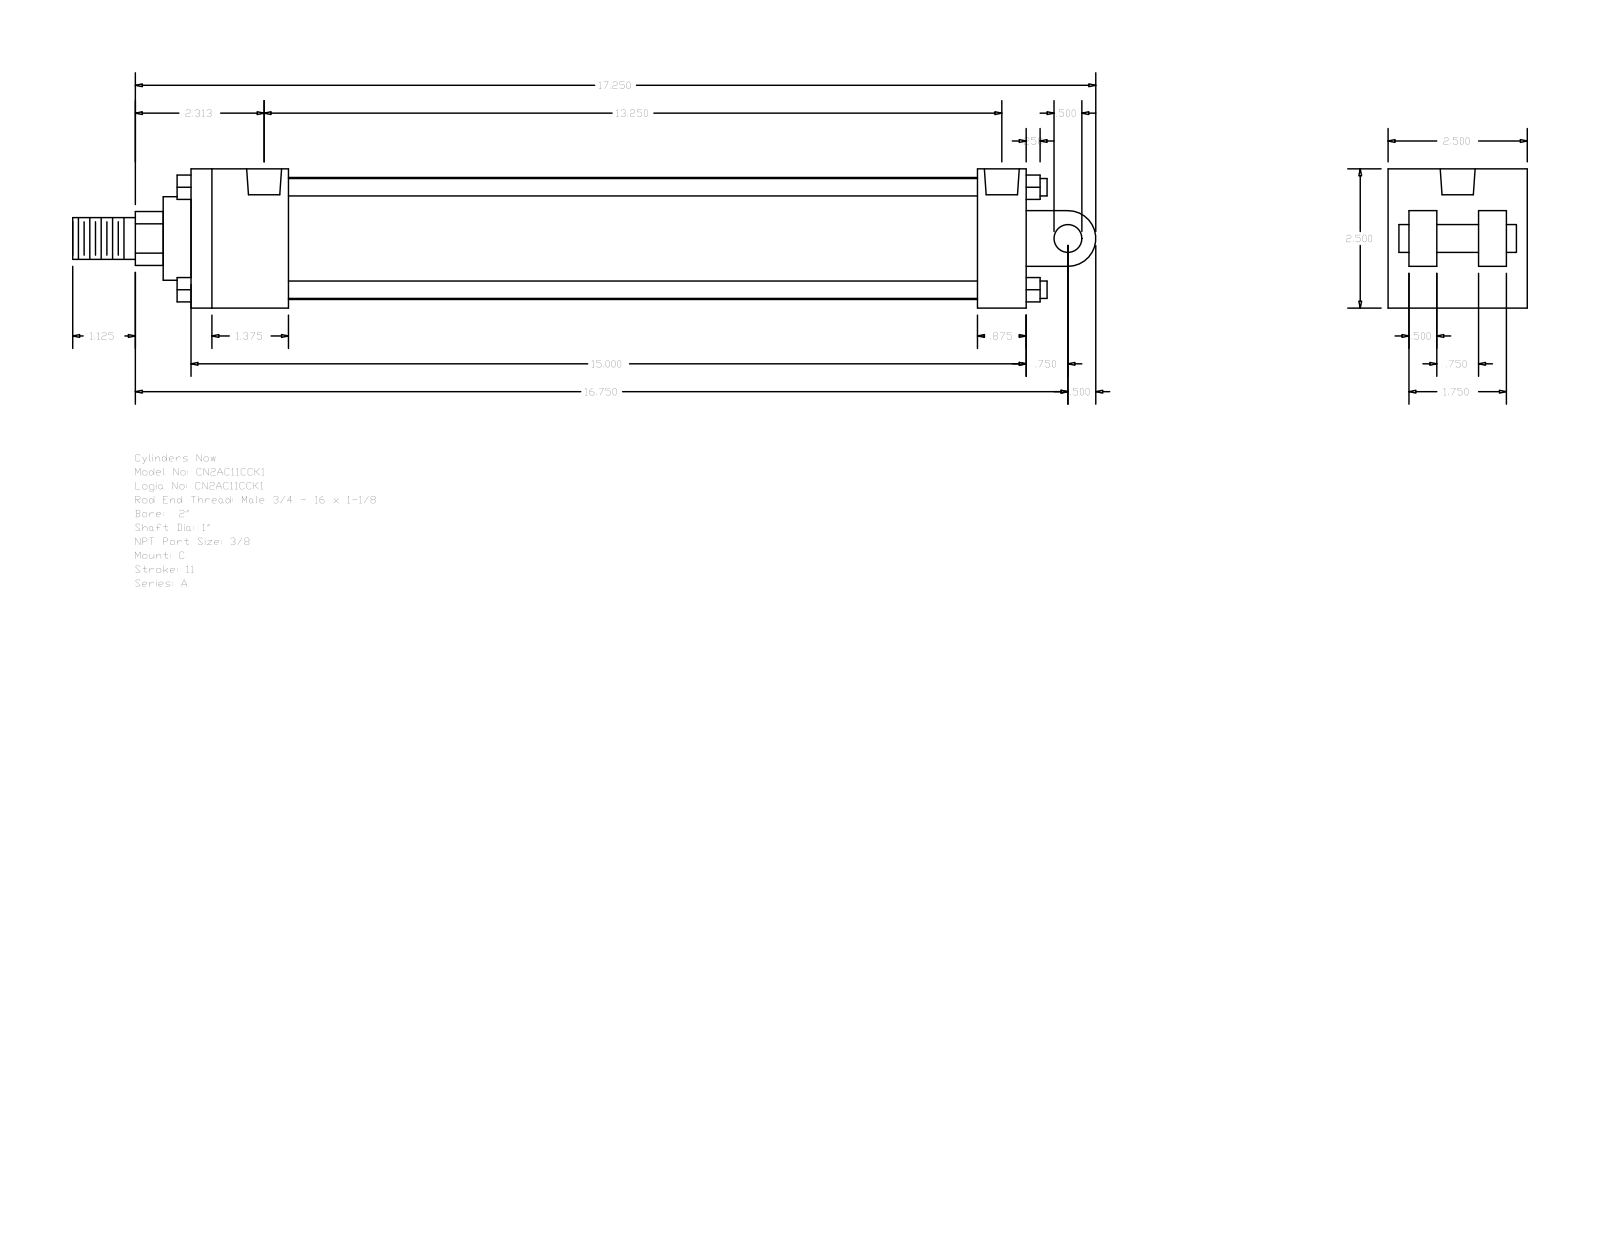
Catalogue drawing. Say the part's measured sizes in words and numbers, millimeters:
The part is named "A_C__0200_1". Its 3-D file was written by "GSSL Pune (CONFIG_CONTROL_DESIGN)". It is 0 solids with 135 faces: 102 planar, 33 cylindrical and 0 other. Overall it measures 466.73 by 63.5 by 63.5 millimeters. Round holes: 4 of diameter 5.56, 2 of diameter 15.93. Round bosses or shafts: 4 of diameter 7.94, 1 of diameter 55.63, 1 of diameter 38.1, 1 of diameter 25.4, 1 of diameter 19.05, 1 of diameter 12.7. Partial cylindrical surfaces (rounded edges, fillets, slot ends): 1 of radius 12.29, 1 of radius 12.7. The main face-to-face distances are 63.5, 22.22, 381, 44.45, 12.7, 336.55, 358.78, 314.33, 9.52, 41.28. The hole center spacings are 330.98, 1.59, 3.98, 332.57, 334.96, 336.55.
